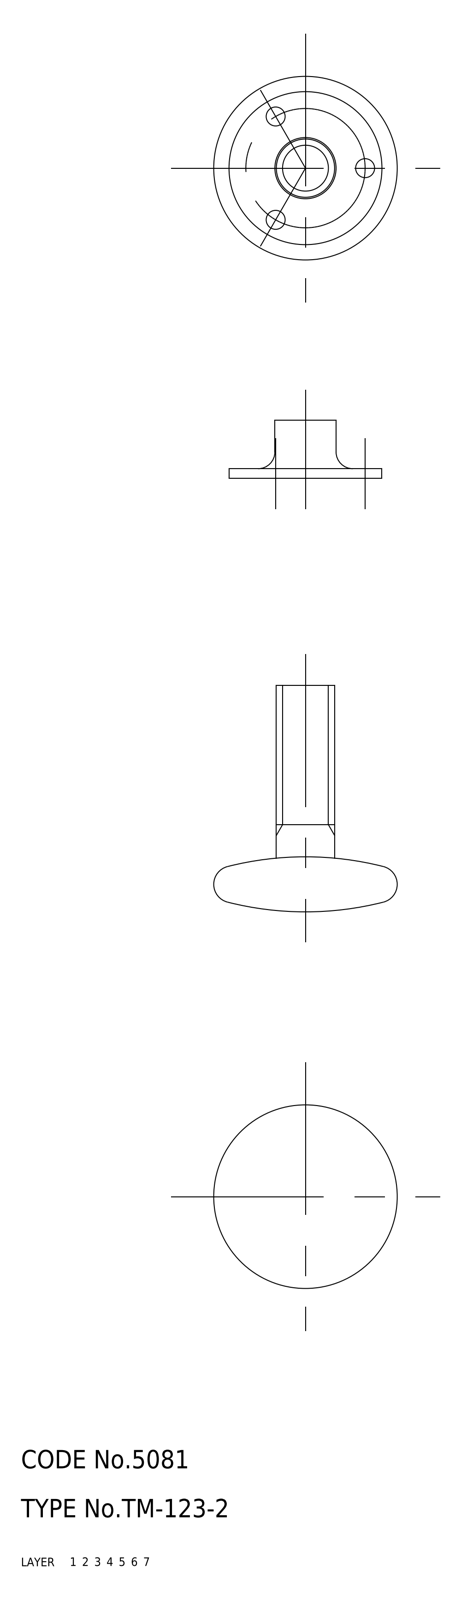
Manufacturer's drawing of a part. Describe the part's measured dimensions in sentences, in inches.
The part is named "nut; foot; bolt; TM_123_2_14454_36". Its 3-D file was written by "CADfix (AUTOMOTIVE_DESIGN)". It is 3 solids with 28 faces: 0 planar, 0 cylindrical and 28 other. Overall it measures 1.457 by 1.181 by 1.181 inches. Its volume is 0.426 cubic inches and its surface area 6.75 square inches.
